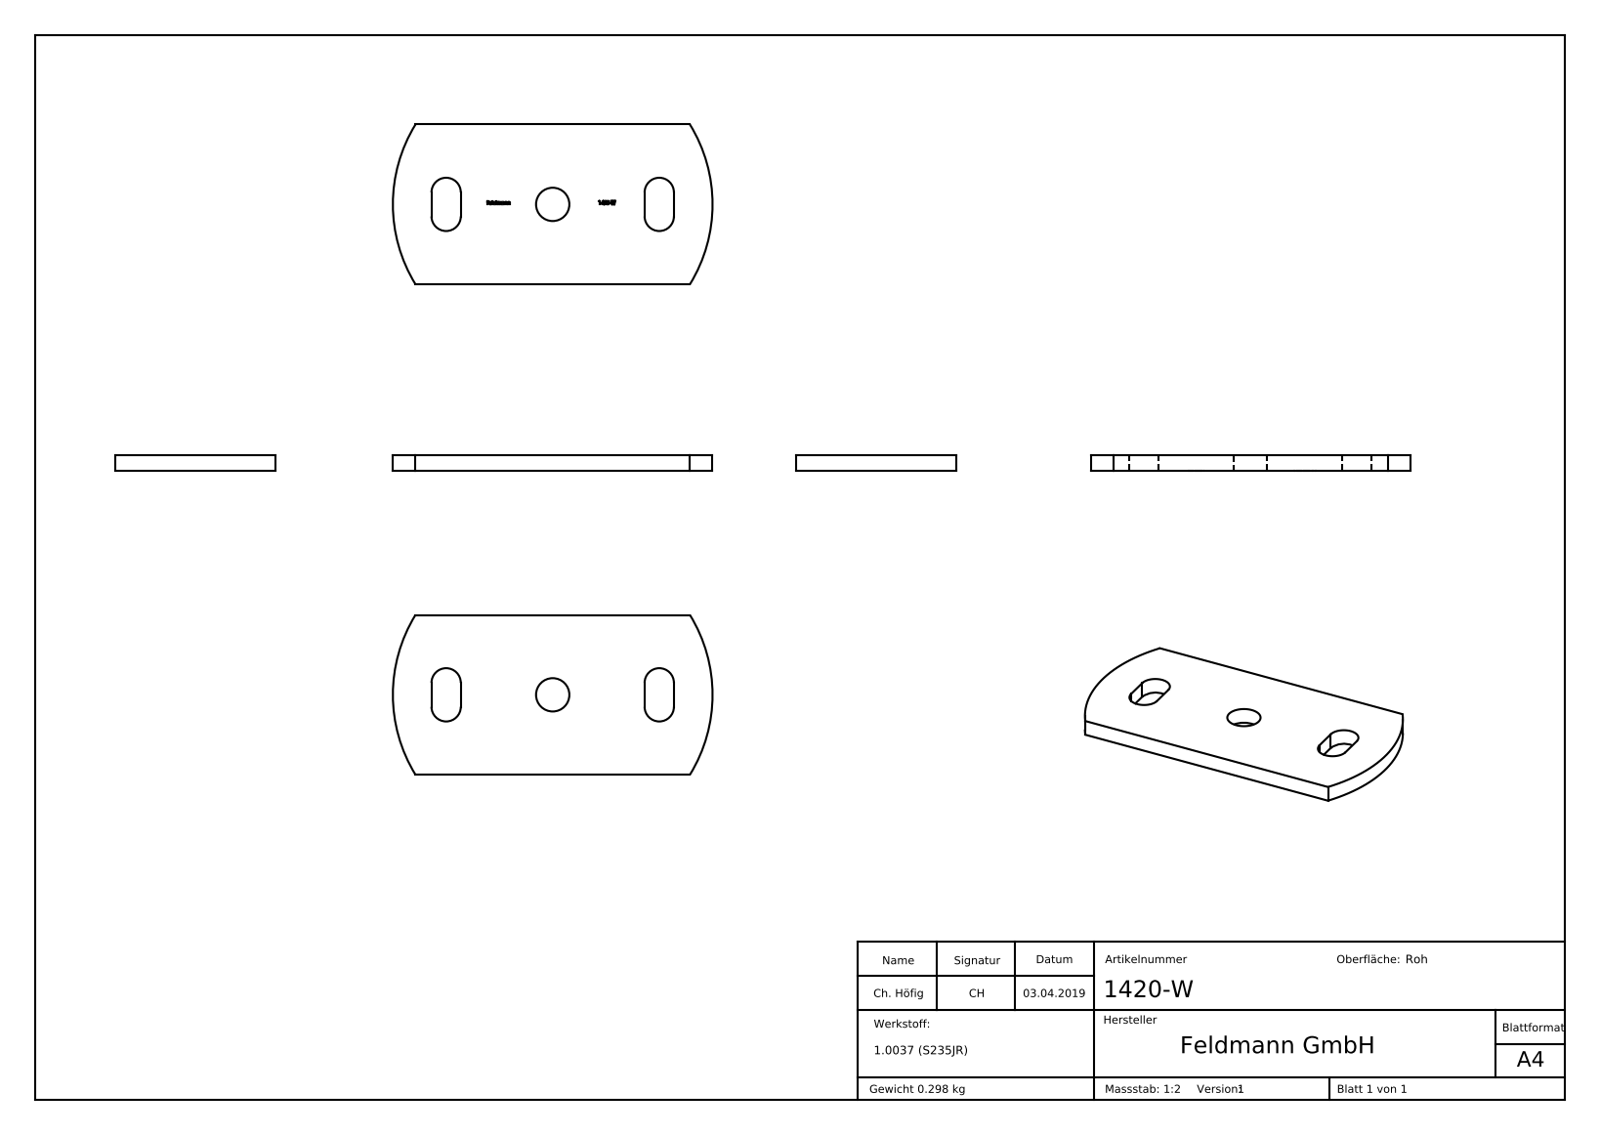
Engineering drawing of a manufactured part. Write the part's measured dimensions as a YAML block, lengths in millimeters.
part_name: "1420-W"
step_written_by: "SolidWorks 2015 (CONFIG_CONTROL_DESIGN)"
units: millimeters
bodies: {solids: 1, faces: 196, planar: 123, cylindrical: 10, other: 63}
overall_size: [120, 60, 6]
volume: 38160
surface_area: 15588
round_holes:
  - {diameter: 12.5, count: 1}
partial_cylinders:
  - {radius: 5.5, count: 4}
  - {radius: 57.19, count: 2}
face_to_face_distances: [6, 60, 11, 80, 91, 69, 5.9, 30, 40.28, 2.02]
